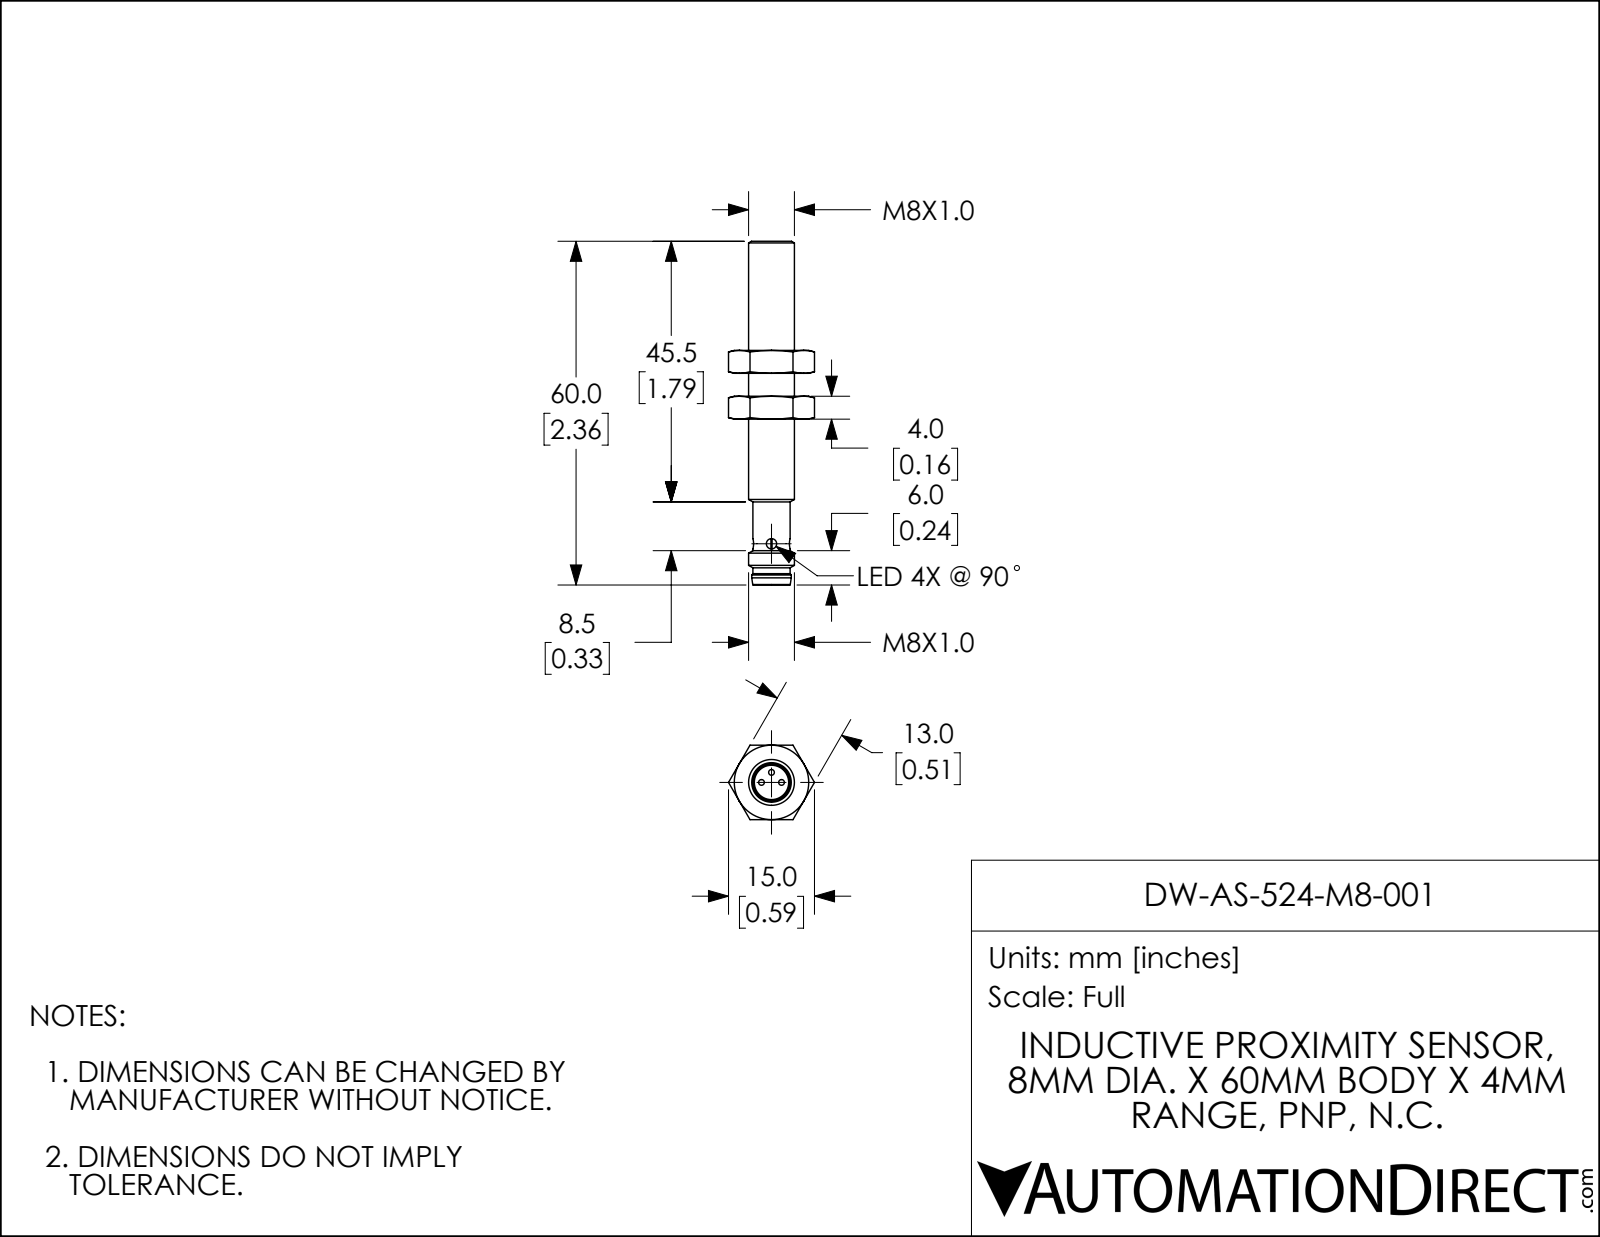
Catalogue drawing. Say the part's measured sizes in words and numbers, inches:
The part is named "DW-AS-524-M8-001". Its 3-D file was written by "SolidWorks 2018 (AUTOMOTIVE_DESIGN)". It is 1 solid with 44 faces: 13 planar, 21 cylindrical and 10 other. Overall it measures 2.362 by 0.315 by 0.315 inches. Its volume is 0.163 cubic inches and its surface area 2.636 square inches. Round holes: 2 of diameter 0.071, 1 of diameter 0.236. Round bosses or shafts: 3 of diameter 0.039, 1 of diameter 0.315, 1 of diameter 0.272, 1 of diameter 0.256. Partial cylindrical surfaces (rounded edges, fillets, slot ends): 1 of radius 0.121. The main face-to-face distances are 2.165, 0.197, 2.362, 0.167, 0.571, 0.374, 1.791, 0.118, 0.079, 0.453.
